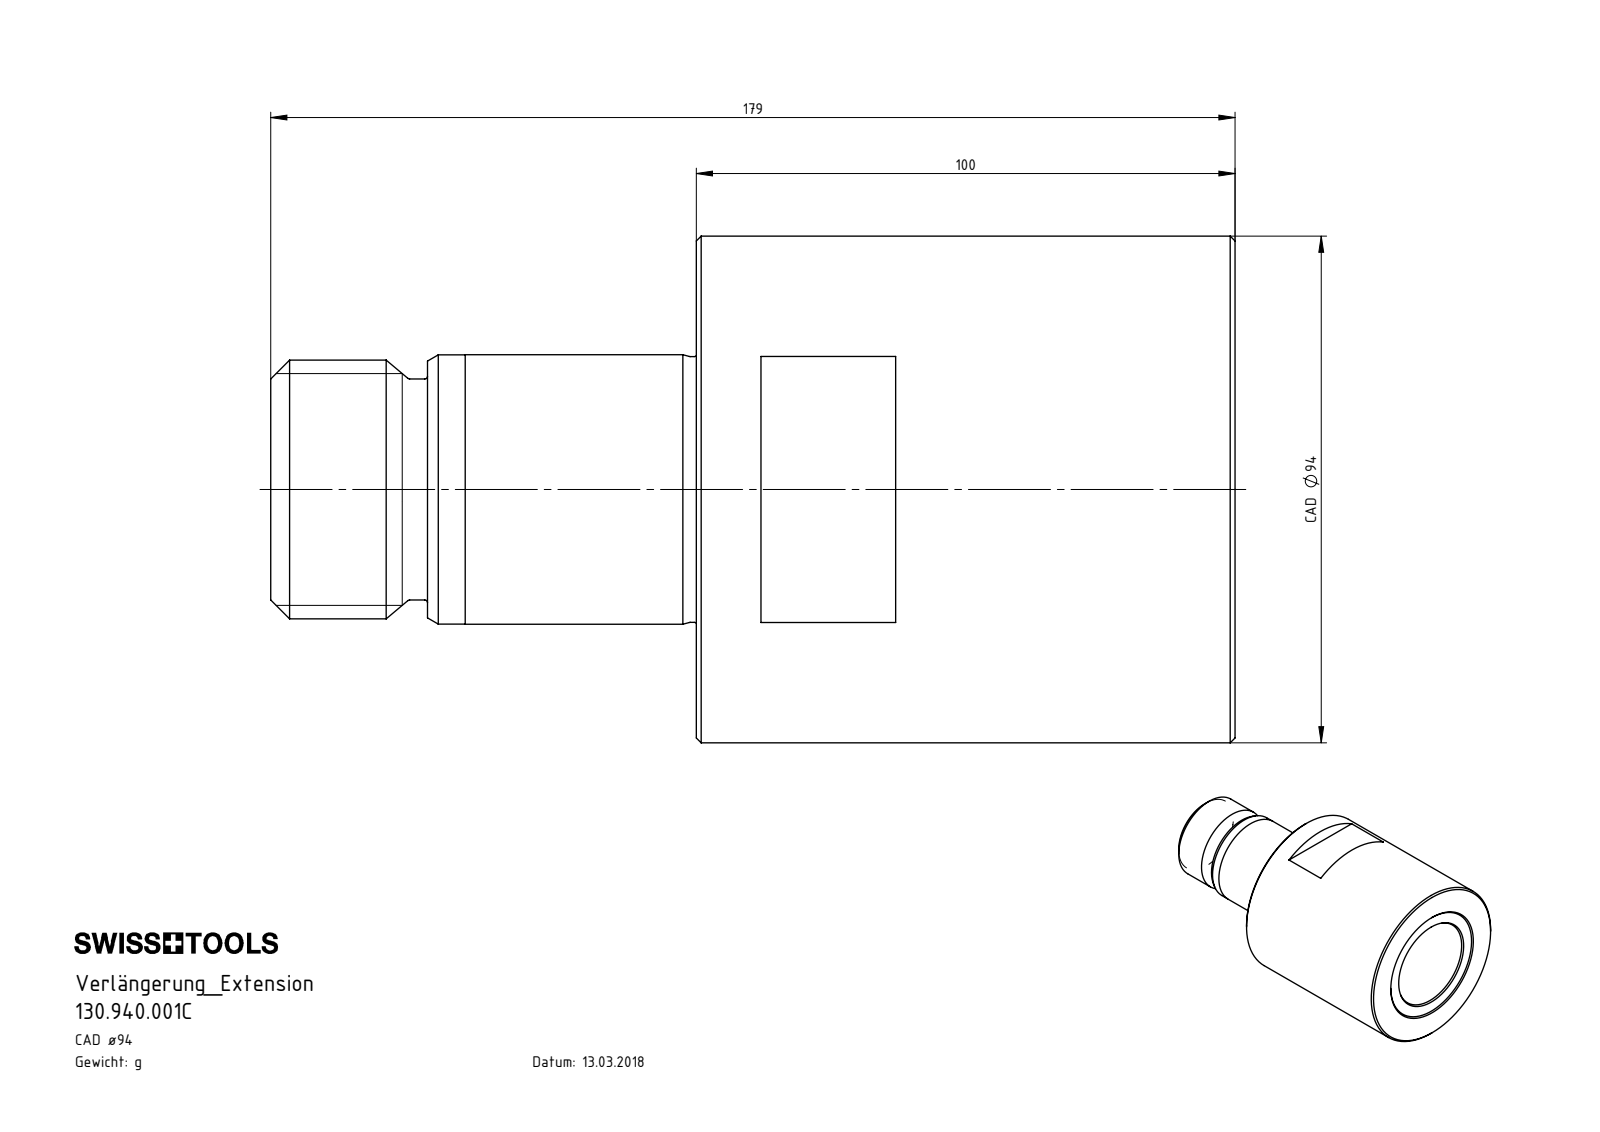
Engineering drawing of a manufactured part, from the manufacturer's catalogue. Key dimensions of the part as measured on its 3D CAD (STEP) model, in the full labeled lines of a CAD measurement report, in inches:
Part name (STEP PRODUCT): 130.940.001C
STEP written by: SolidWorks 2017 (CONFIG_CONTROL_DESIGN)
Units: inches
Bodies: 1 solid, 71 faces (13 planar, 20 cylindrical, 38 other)
Overall size (bounding box): 7.047 × 3.701 × 3.701
Volume: 38.82 in³ · Surface area: 113.6 in²
Round holes (diameter × count): ⌀0.335 ×1, ⌀1.693 ×1, ⌀1.969 ×1, ⌀1.992 ×1
Round bosses / shafts (diameter × count): ⌀3.701 ×1, ⌀1.967 ×1, ⌀1.941 ×1, ⌀1.89 ×1, ⌀1.614 ×1
Main face-to-face distances: 3.937, 3.11, 7.047, 3.15, 7.02, 3.909, 0.028, 3.583, 4.567, 0.472
